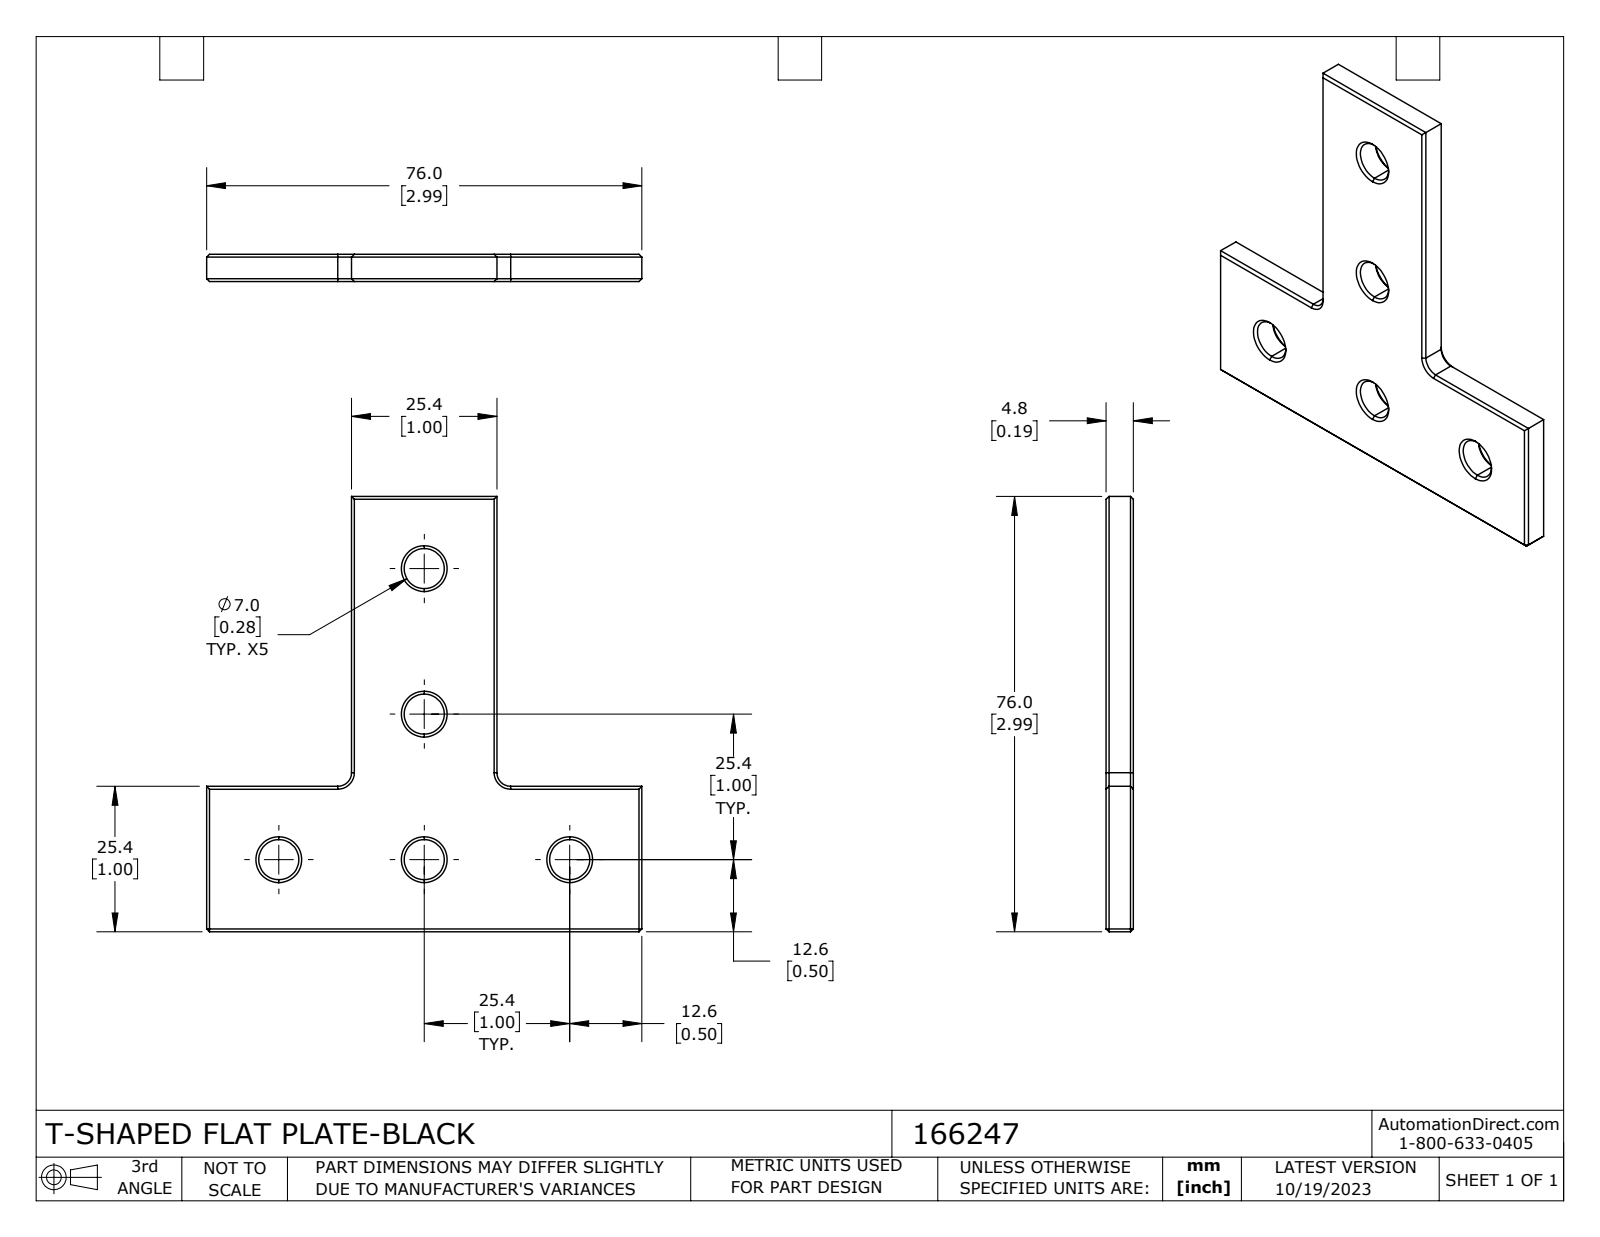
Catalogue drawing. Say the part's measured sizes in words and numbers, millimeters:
The part is named "166247". Its 3-D file was written by "SolidWorks 2023 (CONFIG_CONTROL_DESIGN)". It is 1 solid with 68 faces: 32 planar, 12 cylindrical and 24 other. Overall it measures 76 by 76 by 4.76 millimeters. Its volume is 14 305 cubic millimeters and its surface area 7 771 square millimeters. Round holes: 5 of diameter 7. Partial cylindrical surfaces (rounded edges, fillets, slot ends): 2 of radius 2.39. The main face-to-face distances are 4.76, 25.4, 76, 25.3, 50.7, 20.62, 50.6, 56.39, 35.77, 17.88. The hole center spacings are 25.4, 35.92, 50.8, 56.8.
